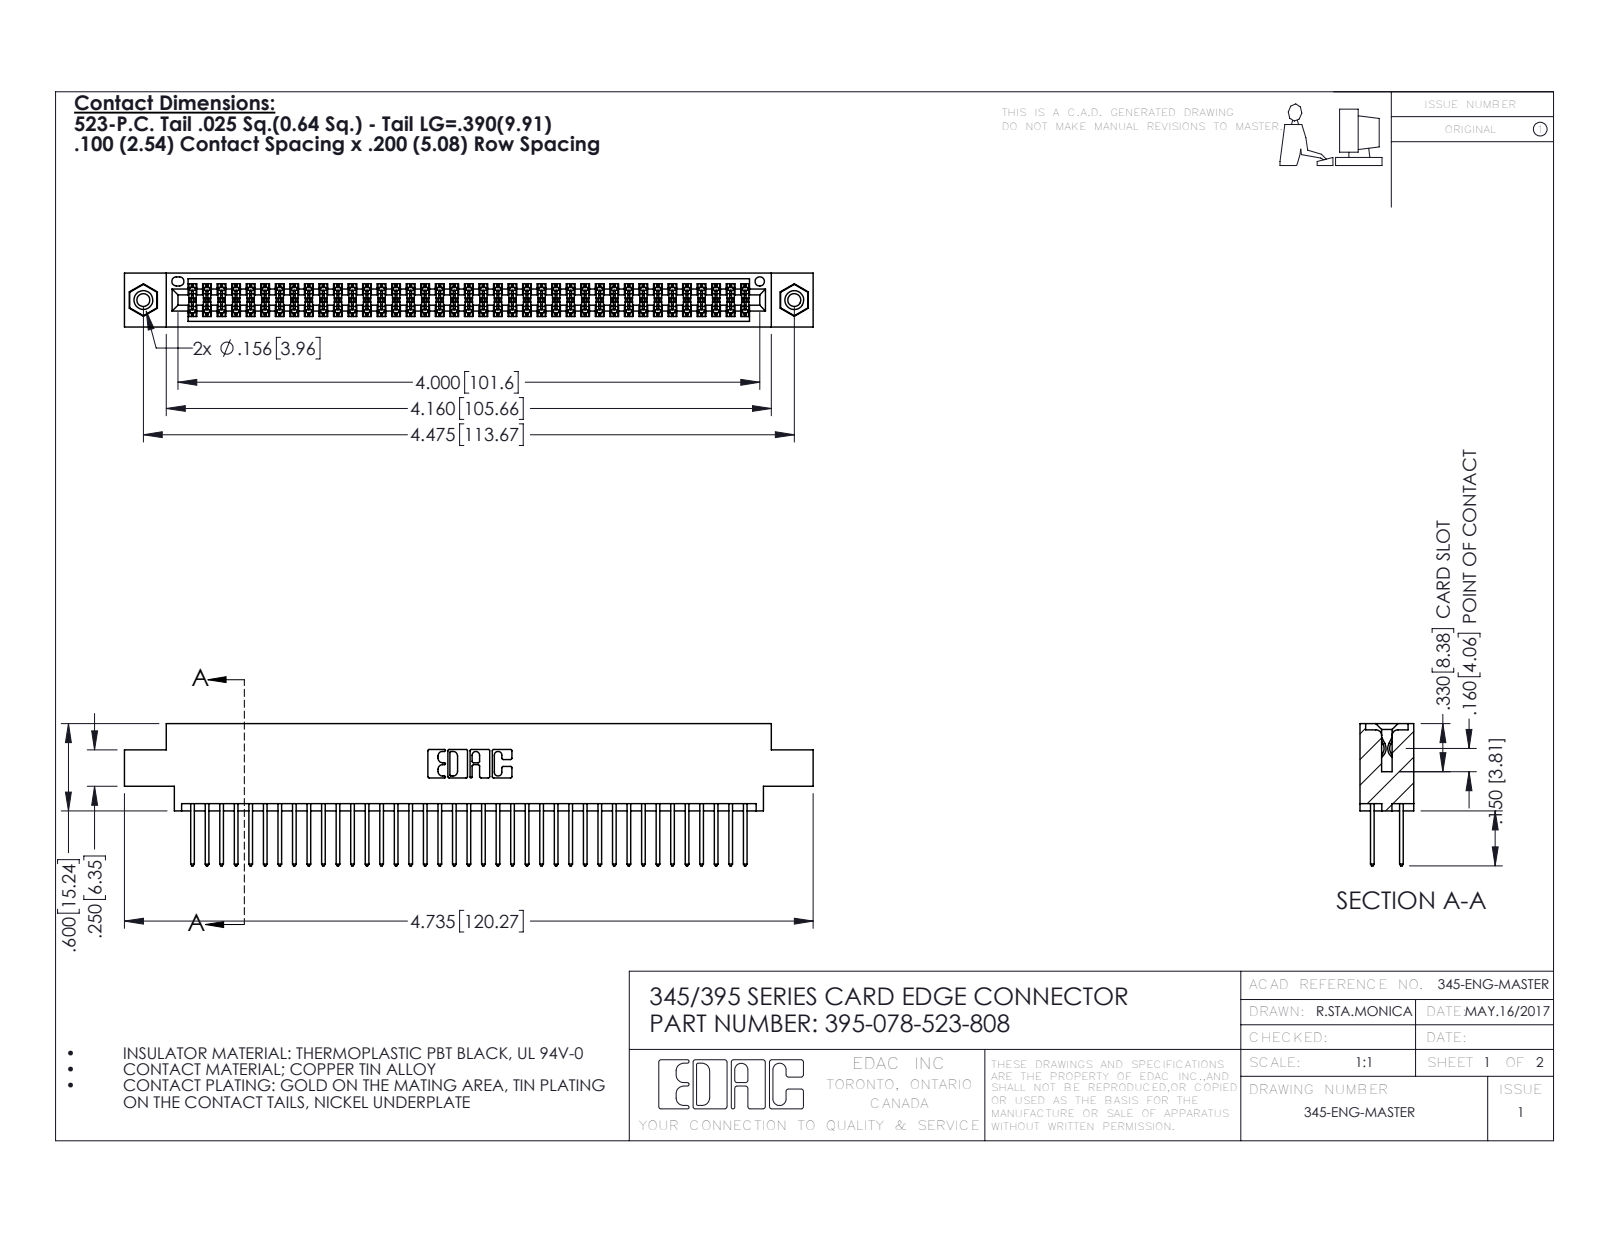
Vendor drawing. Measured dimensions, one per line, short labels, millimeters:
name: 345-292-001_345-293-123; 395-078-523-808; 345 Part_0.170 Offset - 0.156 Dia-TI; 345-250-001_345-250-003-102
written by: SolidWorks 2016 (CONFIG_CONTROL_DESIGN)
unit: mm
bodies: 81 solids, 4090 faces (2690 planar, 1384 cylindrical, 16 other)
size: 120.3 × 24.8 × 9.4
volume: 11 700 mm³; area: 18 100 mm²
holes: 2× ⌀2.3, 2× ⌀3.2, 2× ⌀4, 1× ⌀1.6
bosses: 2× ⌀3.9
rounds: 117× R0.2, 78× R0.3, 22× R0.3, 6× R0.2, 6× R0.8, 3× R0.7, 2× R0.4, 2× R0.5
face distances: 1.8, 7.6, 5.1, 2.5, 6.9, 0.6, 9.4, 5.7, 4.4, 3.8
hole spacings: 6.9, 107.7, 113.7
